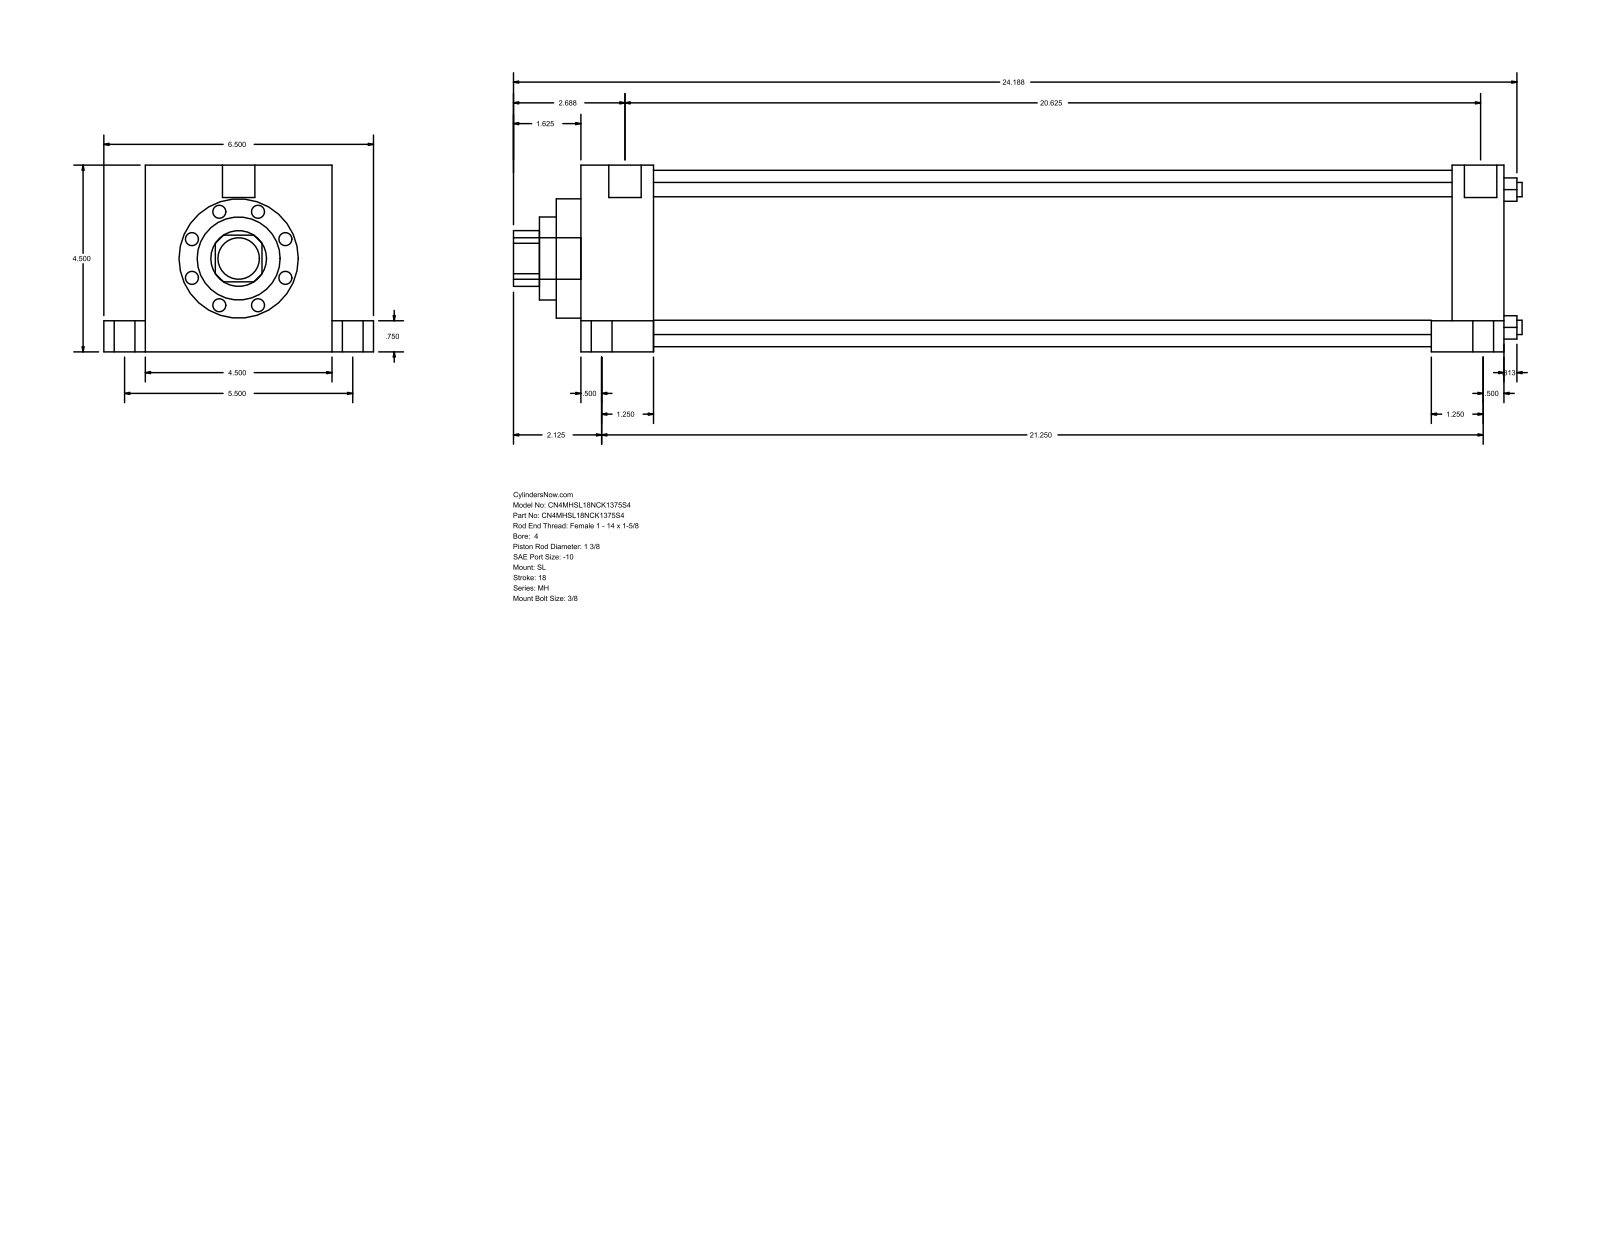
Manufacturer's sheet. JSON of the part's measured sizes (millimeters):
{"part_name": "MH_SL__0400_1.375", "step_written_by": "GSSL Pune (CONFIG_CONTROL_DESIGN)", "units": "millimeters", "bodies": {"solids": 0, "faces": 110, "planar": 77, "cylindrical": 33, "other": 0}, "overall_size": [617.54, 165.1, 114.3], "round_holes": [[8.76, 4], [34.92, 1], [50.8, 1], [73.03, 1], [107.95, 1]], "round_bosses_or_shafts": [[19.05, 4], [12.7, 4], [8.73, 4], [19.84, 2], [25.4, 1]], "partial_cylinders_radius": [[17.06, 1]], "face_to_face_distances": [114.3, 565.15, 44.45, 520.7, 533.4, 488.95, 31.75, 25.4, 139.7, 19.05], "hole_center_spacings": [59.62, 84.32, 119.25]}
